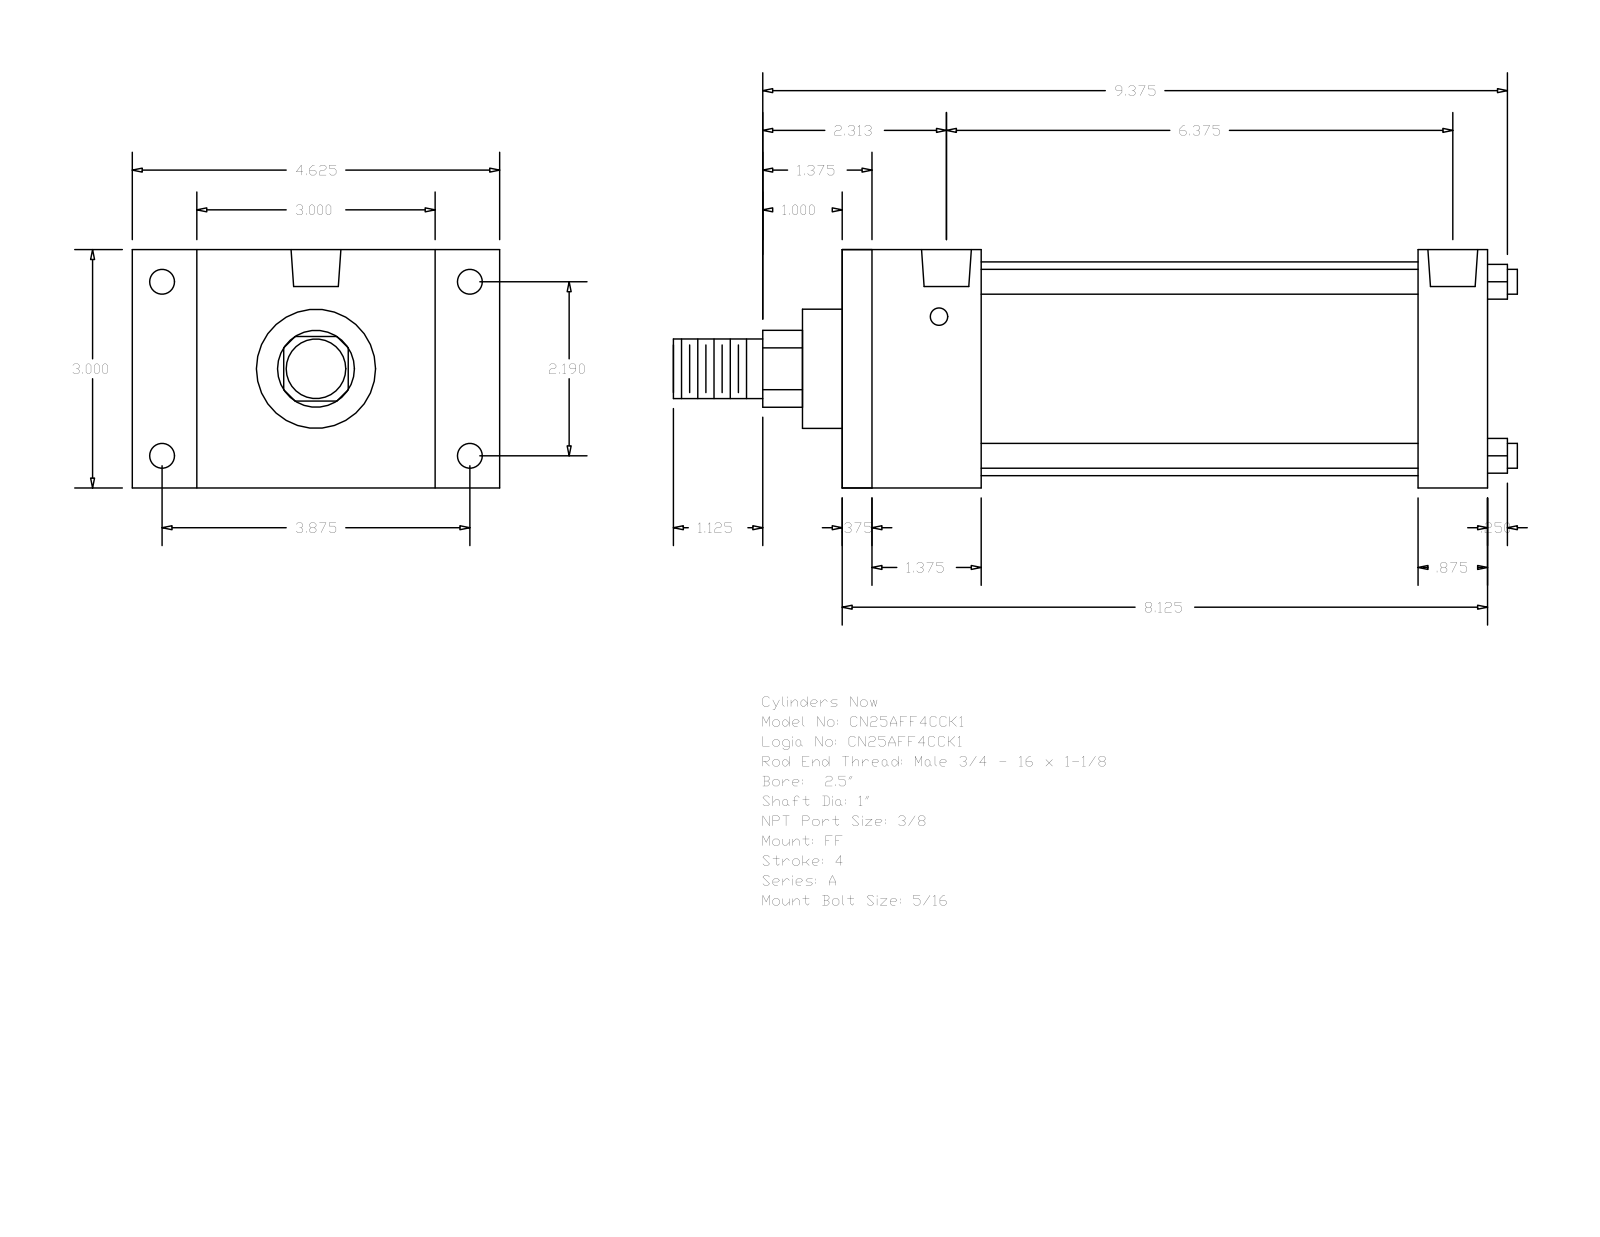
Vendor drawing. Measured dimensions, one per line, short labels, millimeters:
name: A_FF__0250_1
written by: GSSL Pune (CONFIG_CONTROL_DESIGN)
unit: mm
bodies: 0 solids, 92 faces (64 planar, 28 cylindrical, 0 other)
size: 269.88 × 117.47 × 76.2
holes: 4× ⌀5.56, 4× ⌀7.94, 2× ⌀15.93
bosses: 4× ⌀7.94, 1× ⌀68.33, 1× ⌀38.1, 1× ⌀25.4, 1× ⌀19.05
rounds: 1× R12.29
face distances: 76.2, 206.38, 9.52, 196.86, 44.45, 184.15, 34.93, 174.63, 139.7, 161.93
hole spacings: 2.38, 55.62, 98.42, 113.05, 164.3, 166.68, 161.92
